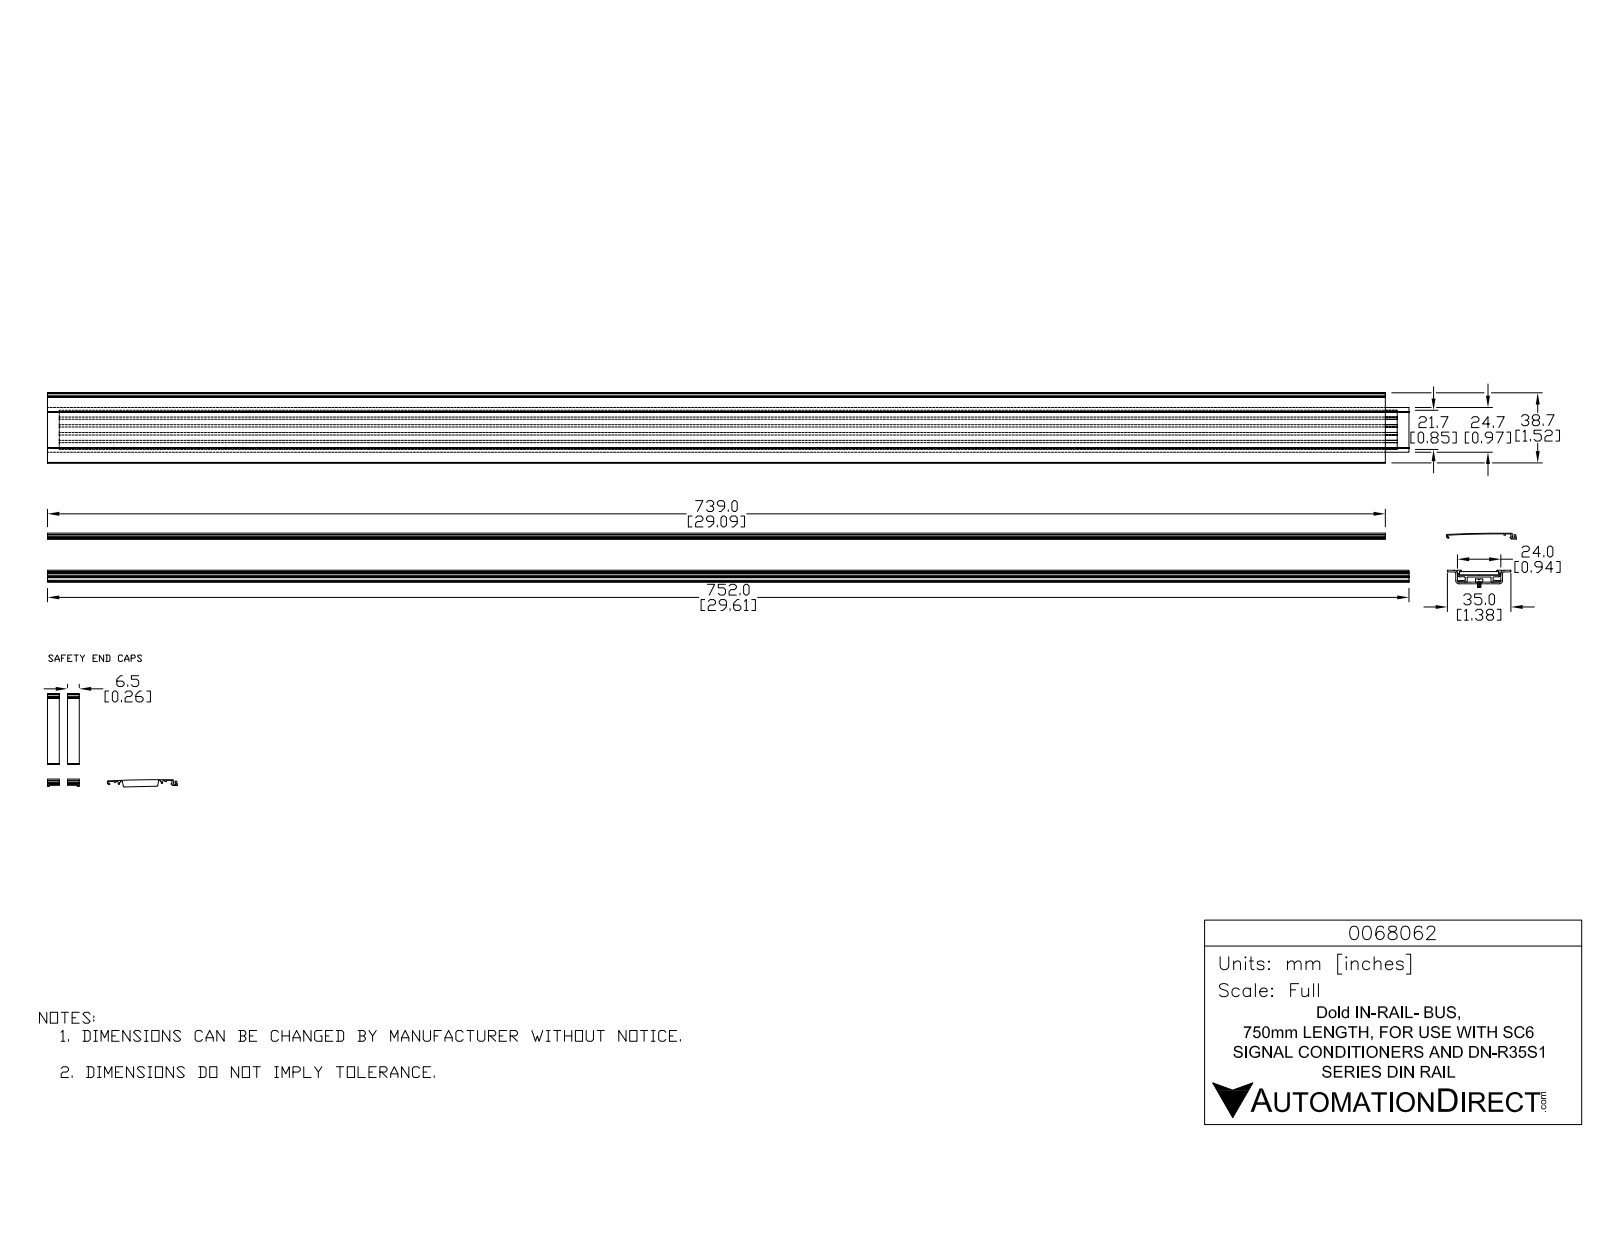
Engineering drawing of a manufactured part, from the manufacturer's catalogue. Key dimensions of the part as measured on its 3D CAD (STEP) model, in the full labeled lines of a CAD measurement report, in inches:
Part name (STEP PRODUCT): POWER BUSS RAIL 750
STEP written by: SolidWorks 2017 (AUTOMOTIVE_DESIGN)
Units: inches
Bodies: 4 solids, 452 faces (378 planar, 74 cylindrical, 0 other)
Overall size (bounding box): 39.665 × 1.525 × 0.687
Volume: 4.482 in³ · Surface area: 270.6 in²
Partial cylindrical surfaces — rounded edges, fillets, slot ends (radius × count): R0.01 ×14, R0.02 ×3, R0.029 ×3, R21.552 ×3, R0.028 ×2, R0.006 ×1, R0.006 ×1, R0.01 ×1
Main face-to-face distances: 0.072, 0.067, 0.039, 0.045, 0.111, 0.107, 0.068, 0.062, 0.143, 0.034
